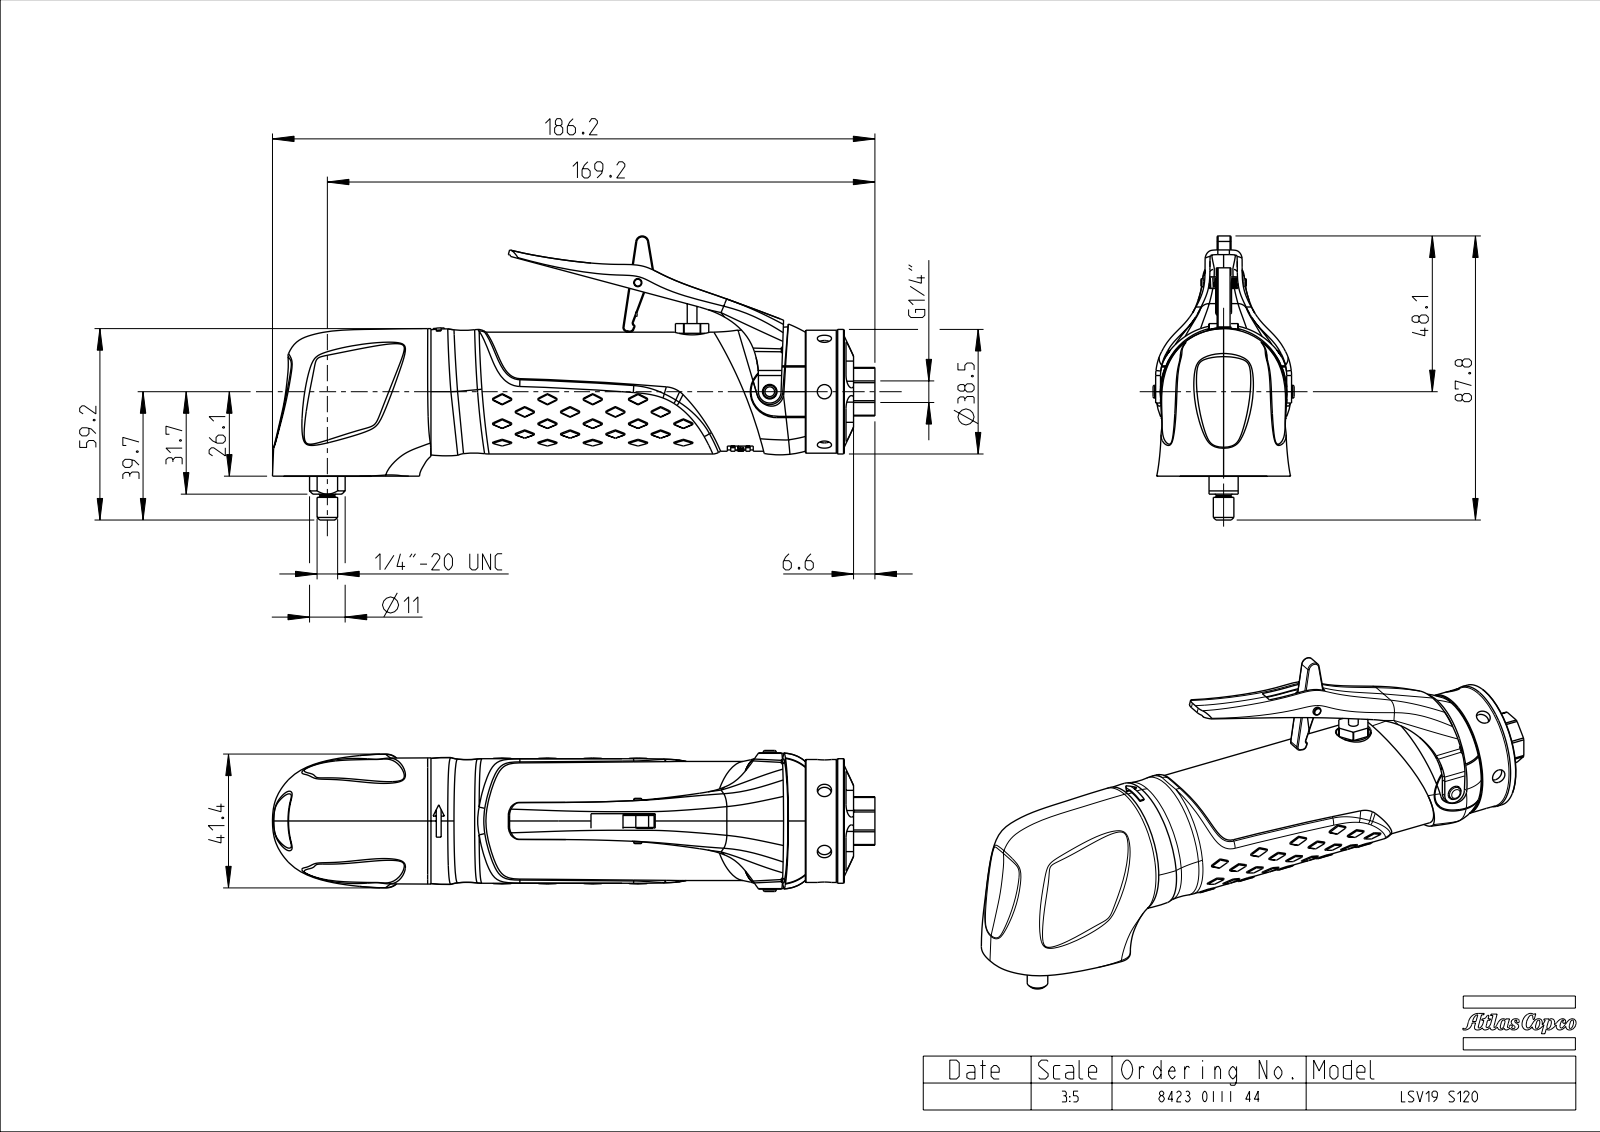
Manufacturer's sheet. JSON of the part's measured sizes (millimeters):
{"part_name": "4150216101; 4150216000; 4150216301; 4150222700 (+8 more)", "step_written_by": "PRO/ENGINEER BY PARAMETRIC TECHNOLOGY CORPORATION, 2011410 (CONFIG_CONTROL_DESIGN)", "units": "millimeters", "bodies": {"solids": 14, "faces": 1660, "planar": 321, "cylindrical": 497, "other": 842}, "overall_size": [186.18, 87.8, 43.6], "volume_mm3": 53778, "surface_area_mm2": 62992, "round_holes": [[1, 114], [3, 3], [4.4, 3], [2.5, 1], [2.7, 1], [4.5, 1], [11, 1], [11.45, 1], [11.7, 1], [14.1, 1], [14.5, 1], [16, 1]], "round_bosses_or_shafts": [[7, 2], [38.5, 1], [38, 1], [36.8, 1], [29.9, 1], [27, 1], [25.7, 1], [21, 1]], "partial_cylinders_radius": [[0.3, 21], [1.75, 10], [3, 8], [0.5, 3], [0.72, 3], [1.2, 3], [0.15, 2], [0.75, 2]], "face_to_face_distances": [126.2, 1, 9.5, 4.5, 10.5, 125.2, 115.7, 12, 5, 5.5], "hole_center_spacings": [2, 4, 5.28, 2.01, 10.5, 6.88, 3.31, 3.46]}
